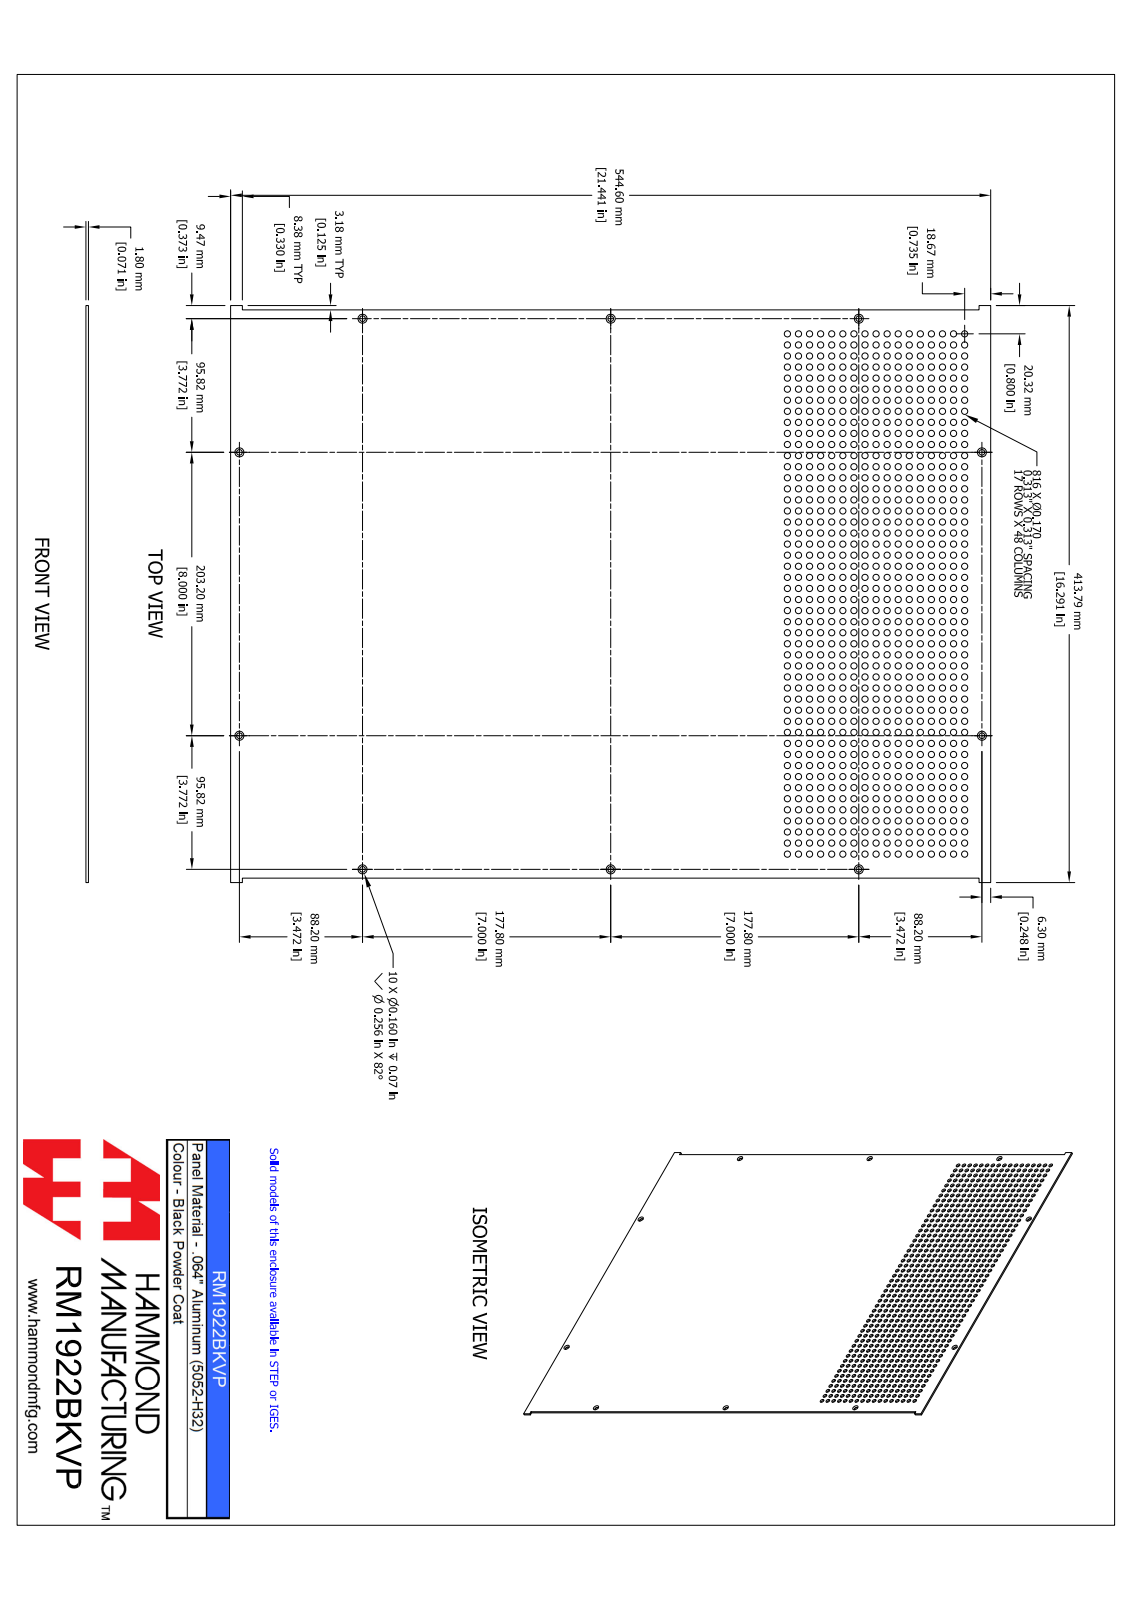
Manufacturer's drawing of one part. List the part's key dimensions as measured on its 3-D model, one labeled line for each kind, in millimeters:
Part name (STEP PRODUCT): RM1922BKVP
STEP written by: SolidWorks 2021 (AUTOMOTIVE_DESIGN)
Units: millimetres
Bodies: 1 solid, 850 faces (14 planar, 826 cylindrical, 10 other)
Overall size (bounding box): 544.6 × 413.8 × 1.8
Volume: 376 600 mm³ · Surface area: 442 300 mm²
Round holes (diameter × count): ⌀4.5 ×816, ⌀4.1 ×10
Main face-to-face distances: 1.8, 407.4, 544.6, 3.2, 410.6, 413.8, 8.4, 536.2, 527.8
Hole centre spacings: 31.8, 8, 23.8, 39.7, 63.5, 15.9, 55.5, 71.5
